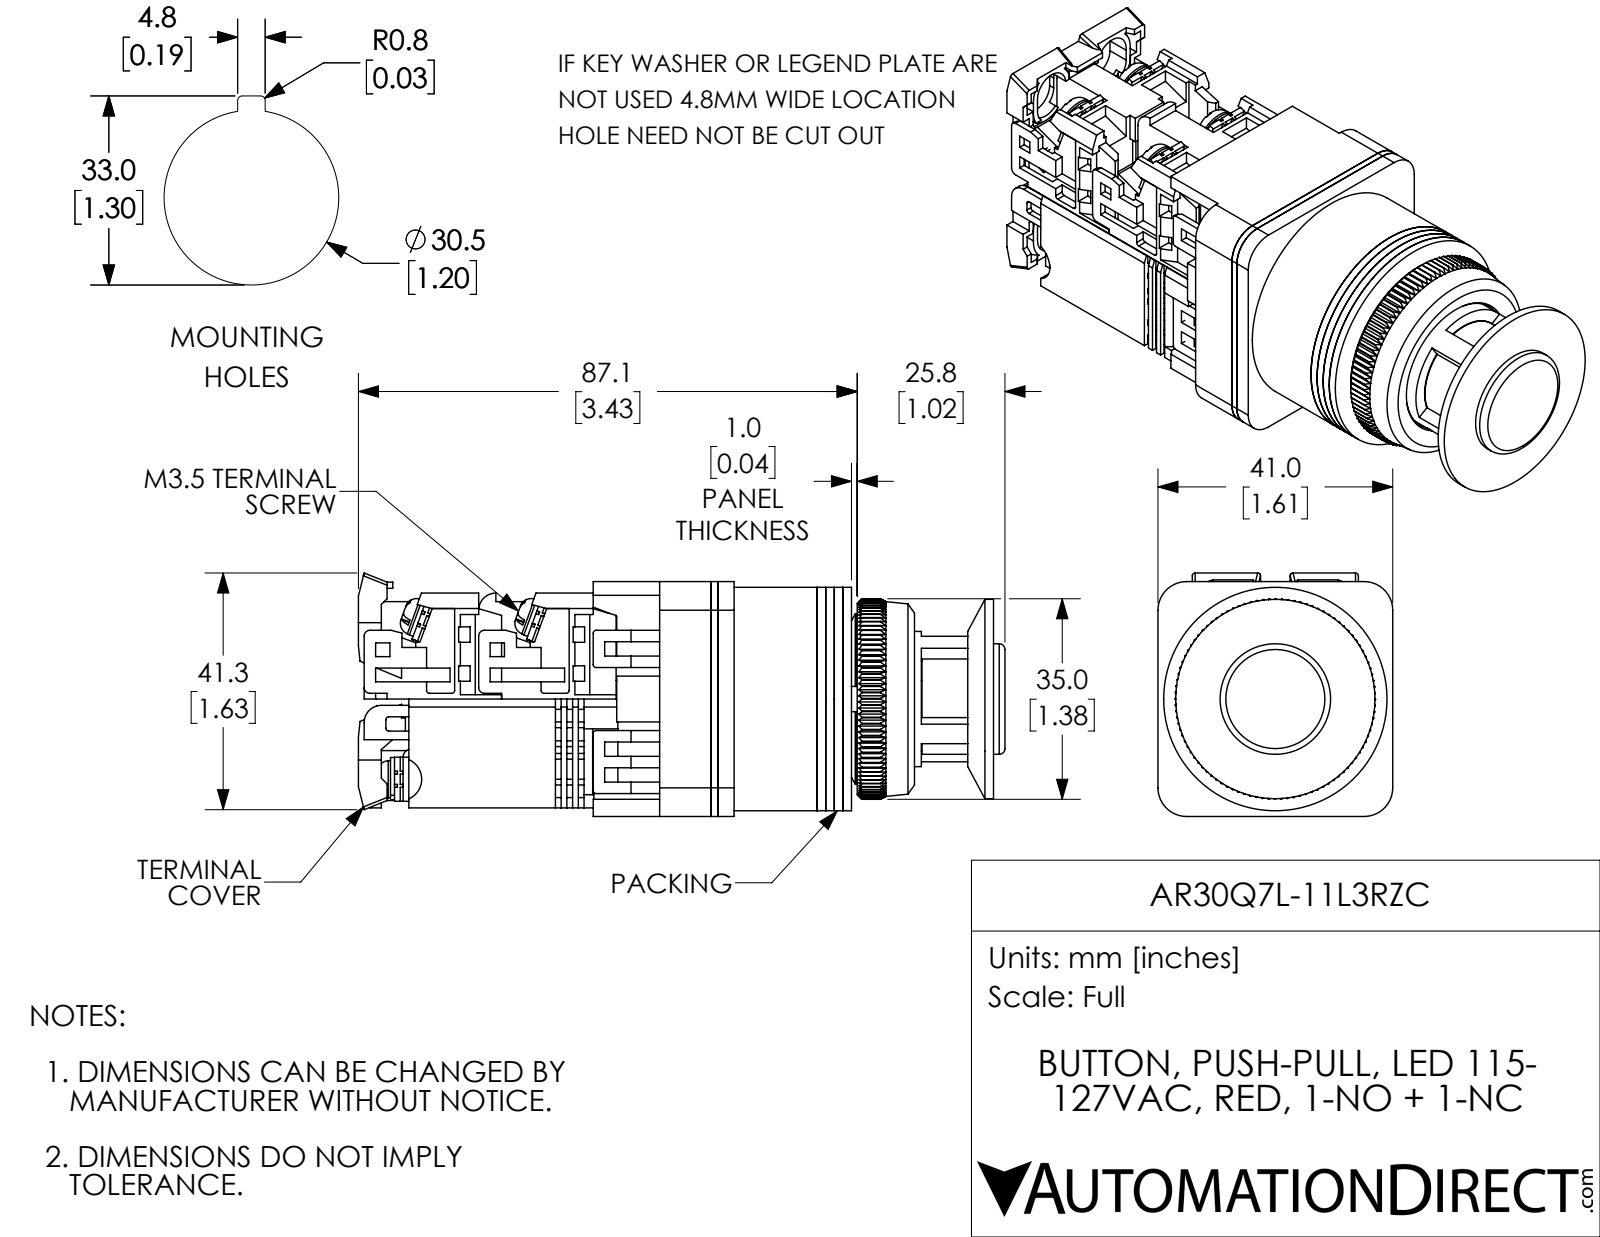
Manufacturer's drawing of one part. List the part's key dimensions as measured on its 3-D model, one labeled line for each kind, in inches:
Part name (STEP PRODUCT): AR30Q7L-11L3RZC
STEP written by: SolidWorks 2017 (AUTOMOTIVE_DESIGN)
Units: inches
Bodies: 36 solids, 2273 faces (1668 planar, 357 cylindrical, 248 other)
Overall size (bounding box): 4.445 × 1.673 × 1.614
Volume: 5.645 in³ · Surface area: 93.36 in²
Round holes (diameter × count): ⌀0.138 ×6, ⌀0.142 ×6, ⌀0.118 ×2, ⌀0.217 ×1, ⌀0.335 ×1, ⌀0.453 ×1, ⌀0.571 ×1, ⌀0.669 ×1, ⌀0.681 ×1, ⌀0.76 ×1, ⌀0.768 ×1, ⌀0.945 ×1
Round bosses / shafts (diameter × count): ⌀0.26 ×6, ⌀0.138 ×4, ⌀1.535 ×1, ⌀1.37 ×1, ⌀1.181 ×1, ⌀1.087 ×1, ⌀0.929 ×1, ⌀0.827 ×1
Partial cylindrical surfaces — rounded edges, fillets, slot ends (radius × count): R0.059 ×25, R0.02 ×21, R0.197 ×5, R0.039 ×4, R0.138 ×4, R0.177 ×4, R0.118 ×3, R0.016 ×1
Main face-to-face distances: 0.059, 0.047, 0.118, 0.858, 0.807, 0.177, 0.74, 0.681, 0.787, 1.614
Hole centre spacings: 0.269, 0.579, 0.624, 0.638, 0.02, 0.583, 0.583, 0.606
